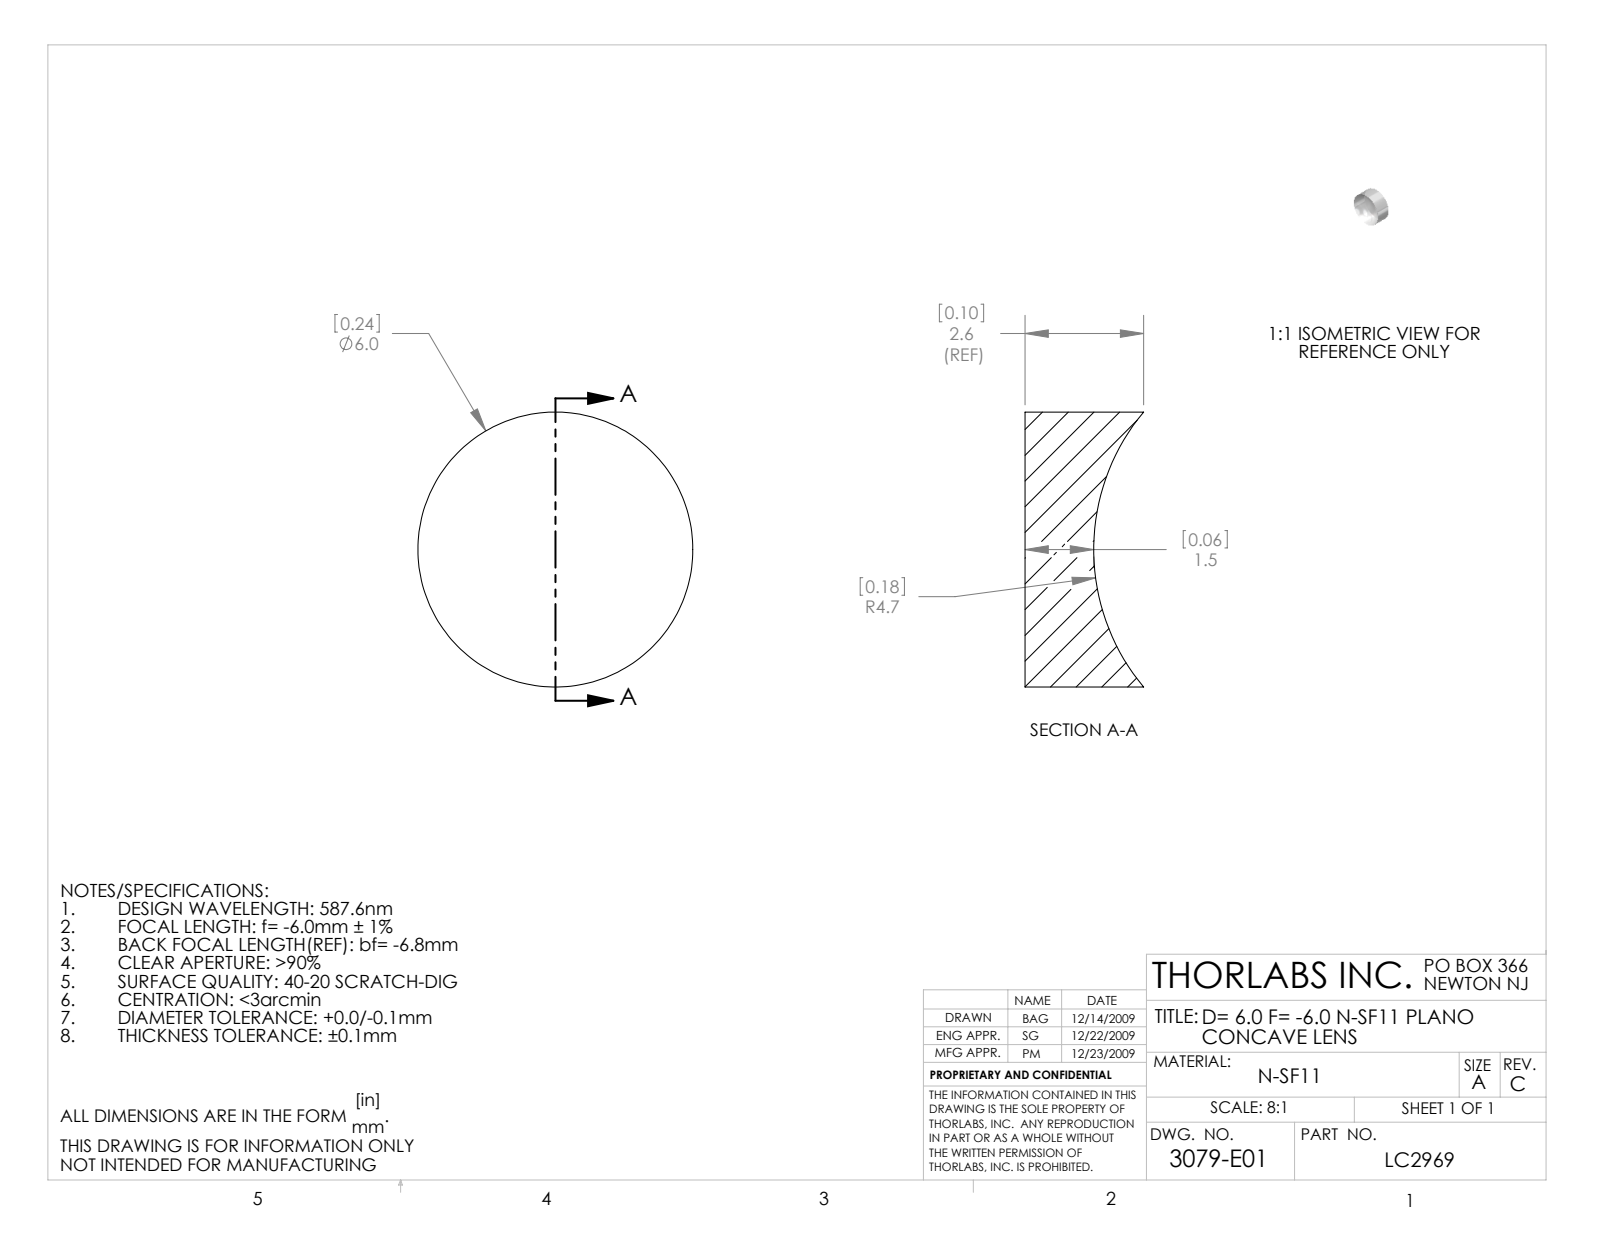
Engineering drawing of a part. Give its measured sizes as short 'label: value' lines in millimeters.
name: 3079-E0W
written by: SolidWorks 2009 (AUTOMOTIVE_DESIGN)
unit: mm
bodies: 1 solid, 5 faces (1 planar, 2 cylindrical, 2 other)
size: 6 × 6 × 2.6
volume: 50 mm³; area: 109 mm²
bosses: 1× ⌀6
